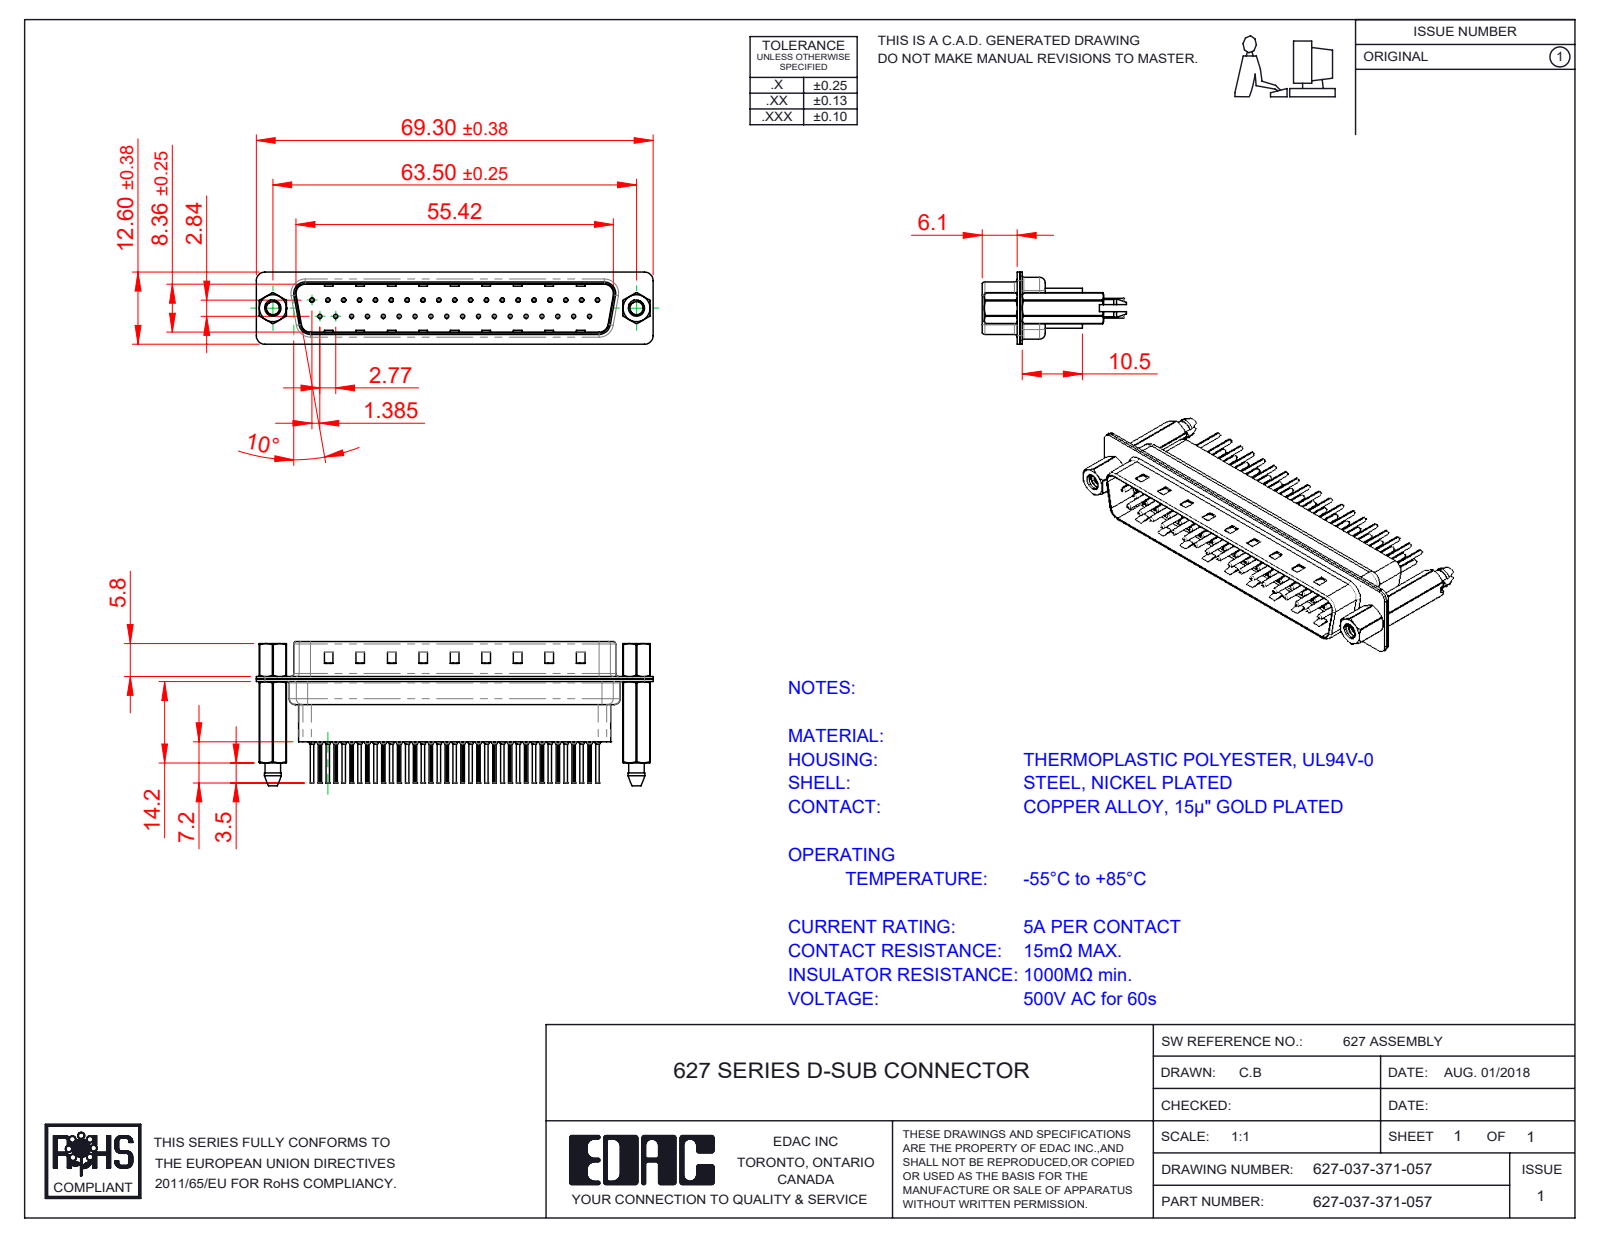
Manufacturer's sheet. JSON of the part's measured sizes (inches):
{"part_name": "627 4-40 Hex Standoff; 627 4-40 Threaded Boardlock_HP71; 627-037-371-057; 627 Housing_37 HP (+4 more)", "step_written_by": "SolidWorks 2020 (CONFIG_CONTROL_DESIGN)", "units": "inches", "bodies": {"solids": 44, "faces": 4272, "planar": 1145, "cylindrical": 1648, "other": 1479}, "overall_size": [2.728, 0.988, 0.496], "volume_in3": 0.361, "surface_area_in2": 23.54, "round_holes": [[0.008, 37], [0.014, 37], [0.043, 37], [0.063, 37], [0.089, 2], [0.09, 2], [0.157, 2], [0.189, 2]], "round_bosses_or_shafts": [[0.079, 37], [0.059, 37], [0.03, 37], [0.024, 37], [0.193, 2], [0.11, 2]], "partial_cylinders_radius": [[0.004, 74], [0.059, 18], [0.079, 12], [0.063, 10], [0.02, 8], [0.01, 4], [0.024, 4], [0.026, 4]], "face_to_face_distances": [0.016, 0.032, 0.377, 0.018, 0.027, 0.302, 0.059, 0.043, 0.318, 0.345], "hole_center_spacings": [0.124, 0.109, 0.218, 0.327, 0.198, 0.398, 0.436, 0.503]}
